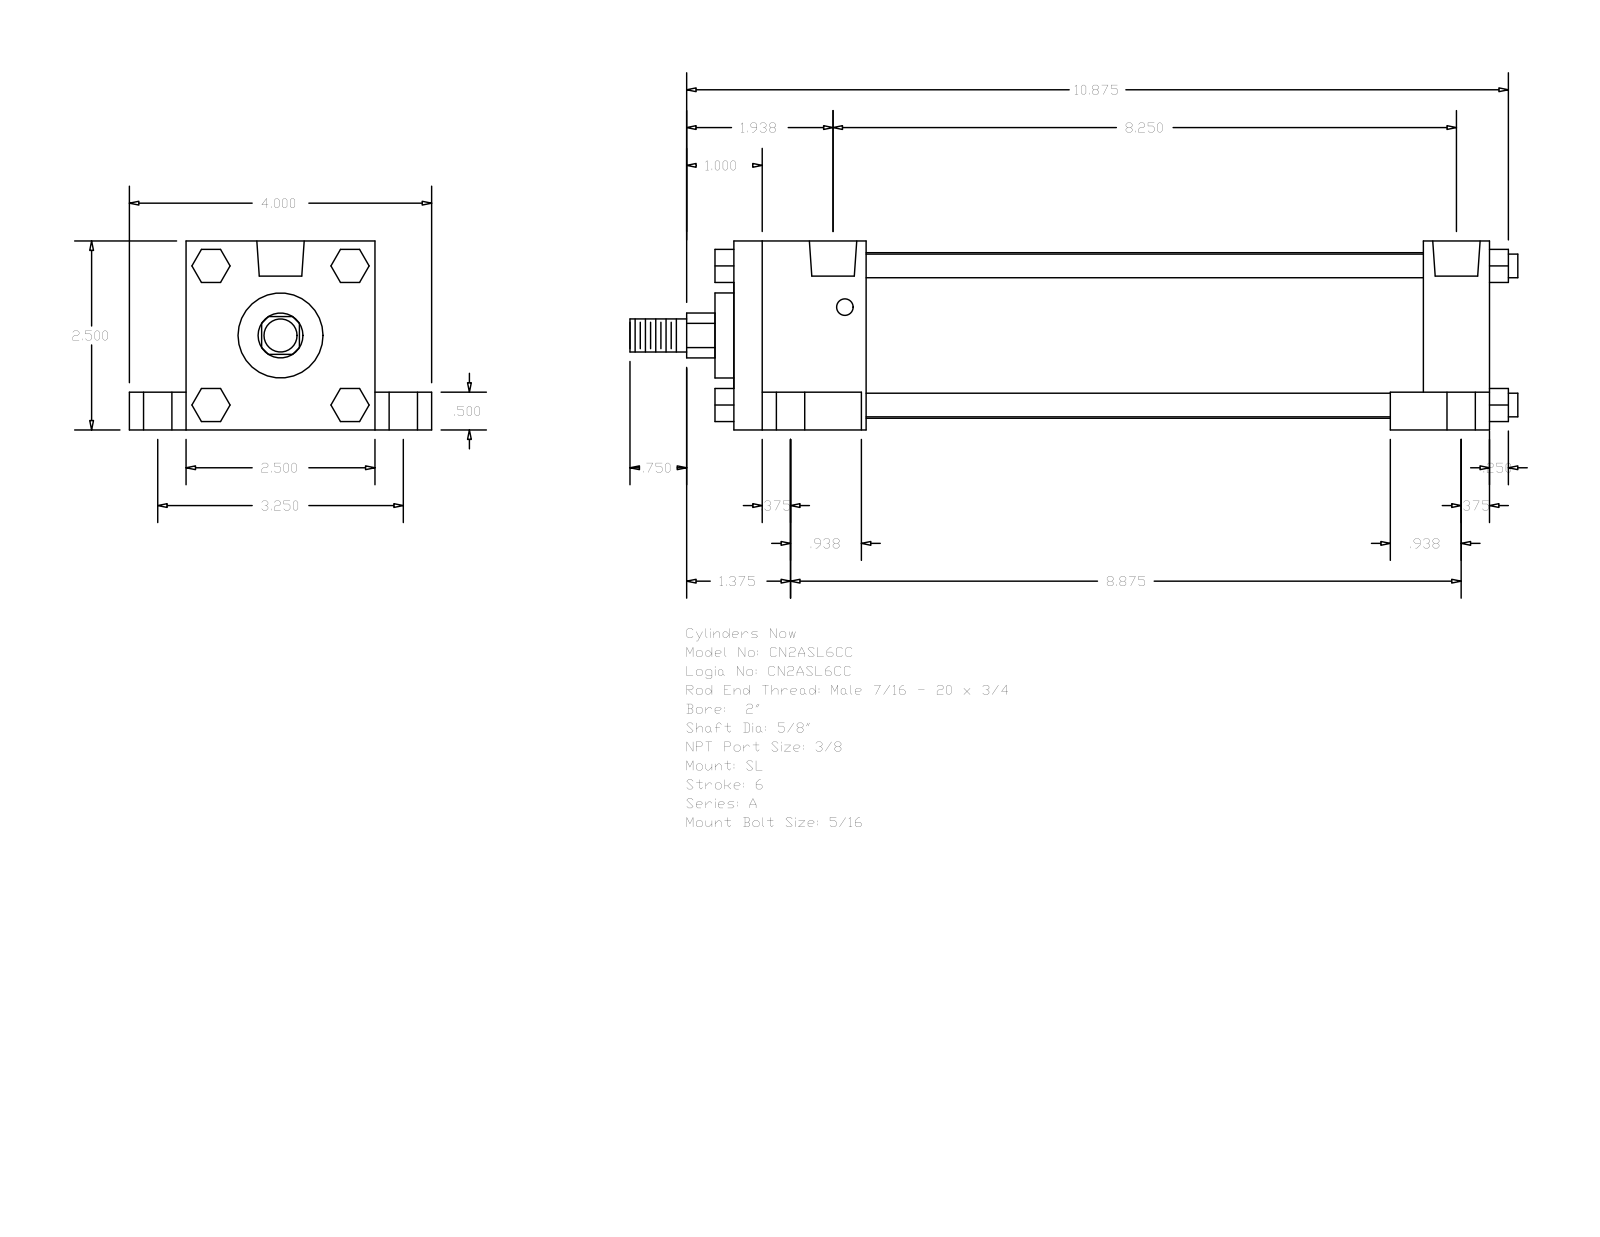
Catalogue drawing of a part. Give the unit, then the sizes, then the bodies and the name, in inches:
Units: inches
Overall size (bounding box): 11.75 × 4 × 2.5
Round holes (diameter × count): ⌀0.219 ×4, ⌀0.375 ×4, ⌀0.625 ×4, ⌀0.627 ×2
Round bosses / shafts (diameter × count): ⌀0.313 ×4, ⌀2.19 ×1, ⌀1.125 ×1, ⌀0.625 ×1, ⌀0.437 ×1
Partial cylindrical surfaces — rounded edges, fillets, slot ends (radius × count): R0.297 ×1
Main face-to-face distances: 2.5, 10, 2, 0.5, 0.75, 3.25, 1.75, 8.25, 9.125, 7.375
Hole centre spacings: 1.626, 1.639, 1.719, 1.777, 3.25, 7.937, 8.316, 8.47
Bodies: 0 solids, 148 faces (112 planar, 36 cylindrical, 0 other)
Part name (STEP PRODUCT): A_SL__0200_0.625
STEP written by: GSSL Pune (CONFIG_CONTROL_DESIGN)
